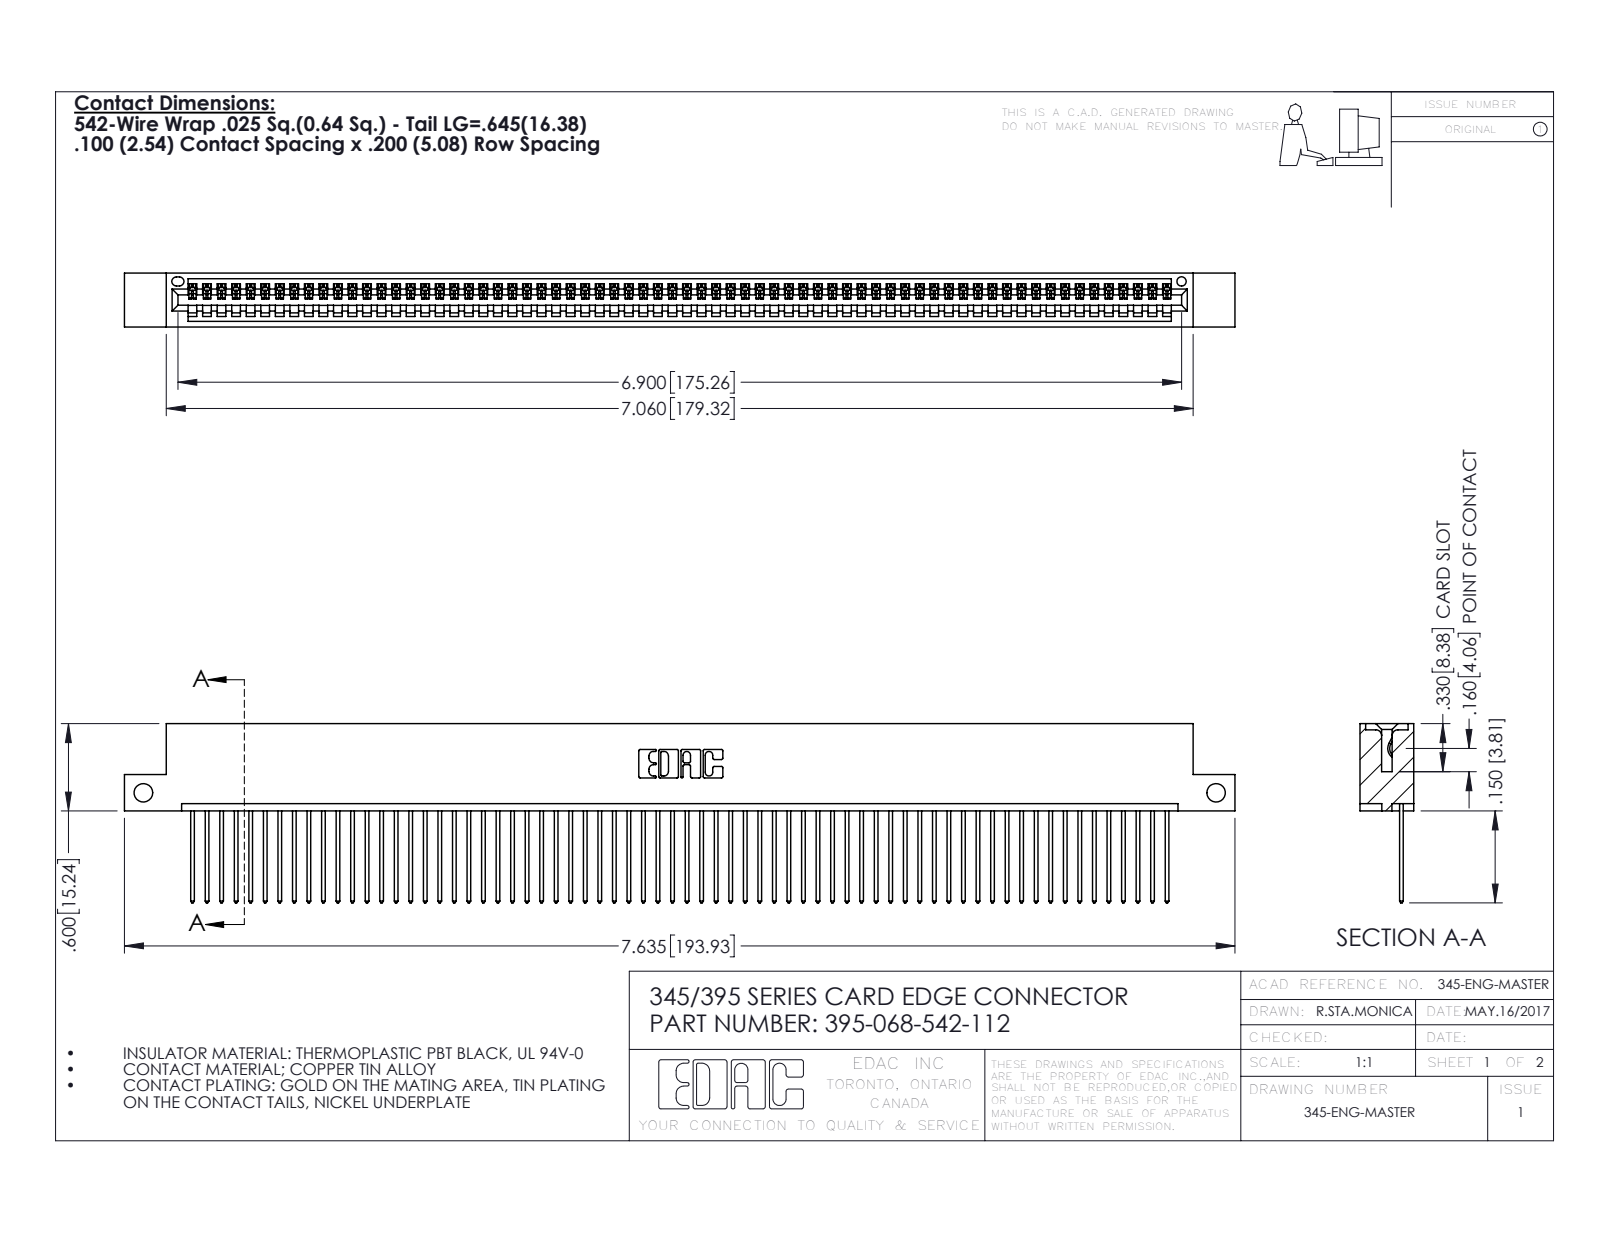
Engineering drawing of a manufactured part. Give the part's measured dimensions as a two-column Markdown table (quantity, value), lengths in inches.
| quantity | value |
| --- | --- |
| part name | 345-292-001_345-293-142; 345 Part_Flush Mounting Lugs - Side Mount; 395-068-542-112 |
| STEP written by | SolidWorks 2016 (CONFIG_CONTROL_DESIGN) |
| units | inches |
| bodies | 69 solids, 4070 faces (2800 planar, 1270 cylindrical, 0 other) |
| overall size | 7.635 × 1.232 × 0.37 |
| volume | 1.141 in³ |
| surface area | 40.32 in² |
| round holes (diameter × count) | 0.128 × 2, 0.064 × 1 |
| partial cylindrical surfaces (radius × count) | 0.006 × 136, 0.01 × 136, 0.01 × 22, 0.007 × 6, 0.031 × 6, 0.026 × 3, 0.031 × 2, 0.04 × 2 |
| main face-to-face distances | 0.072, 0.298, 0.098, 0.272, 0.025, 0.37, 0.2, 0.225, 0.149, 0.072 |
| hole center spacings | 7.375 |
